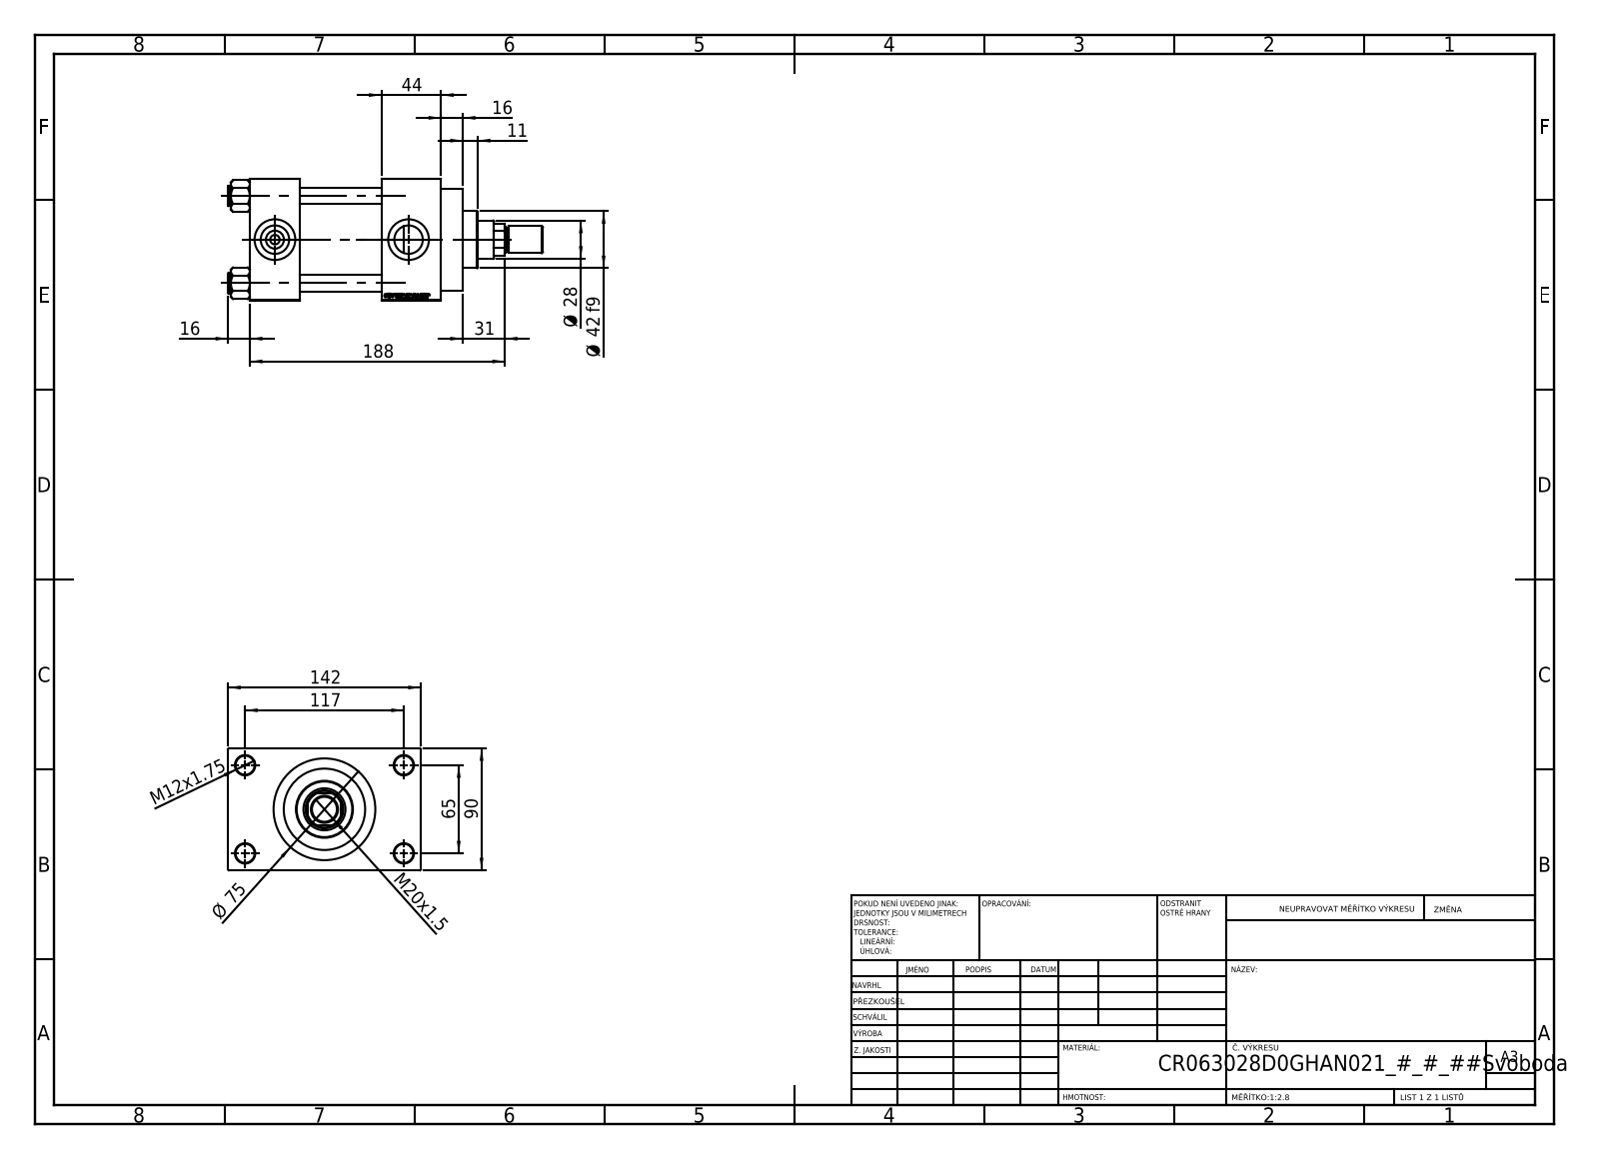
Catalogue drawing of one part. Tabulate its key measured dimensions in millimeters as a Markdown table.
| quantity | value |
| --- | --- |
| part name | V215CR_D_Body; V215CR_VCP_D; ROD_END_AH; V215CR_D_TYCINKA (+2 more) |
| STEP written by | SolidWorks 2019 (CONFIG_CONTROL_DESIGN) |
| units | millimeters |
| bodies | 12 solids, 1117 faces (501 planar, 92 cylindrical, 524 other) |
| overall size | 232 × 142 × 90 |
| volume | 1 107 000 mm³ |
| surface area | 203 400 mm² |
| round holes (diameter × count) | 12 × 4, 14 × 4, 7 × 2, 20.96 × 2, 30 × 2, 18.5 × 1, 28 × 1, 31 × 1, 50 × 1, 60 × 1, 63 × 1 |
| round bosses / shafts (diameter × count) | 15 × 4, 75 × 1, 69 × 1, 42 × 1, 20 × 1, 18 × 1 |
| partial cylindrical surfaces (radius × count) | 13.5 × 1 |
| main face-to-face distances | 90, 60, 37, 97, 104, 141, 44, 26, 116, 16 |
| hole center spacings | 26.35, 45.47, 64.3, 66.92, 69.81, 90.65, 111.34, 65 |
